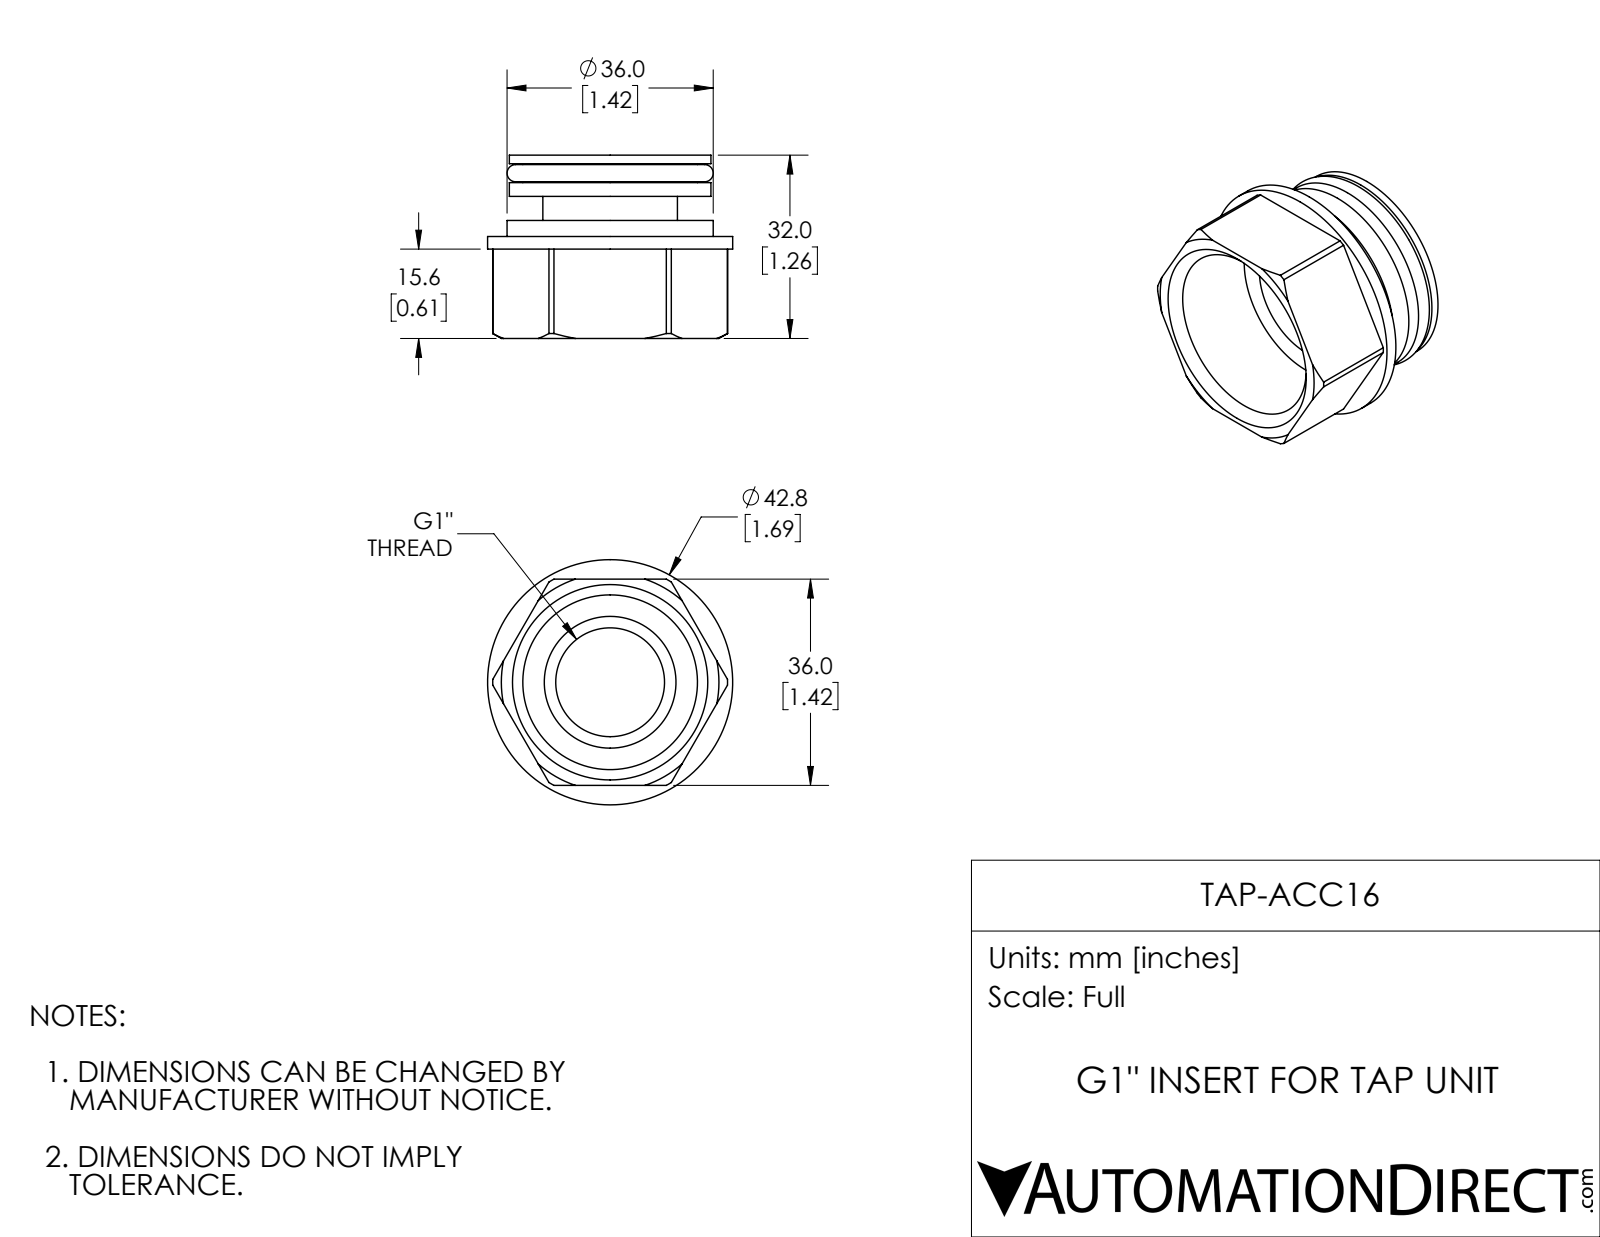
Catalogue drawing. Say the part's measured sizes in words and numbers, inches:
The part is named "TAP-ACC16". Its 3-D file was written by "SolidWorks 2017 (AUTOMOTIVE_DESIGN)". It is 1 solid with 58 faces: 15 planar, 26 cylindrical and 17 other. Overall it measures 1.685 by 1.685 by 1.26 inches. Its volume is 0.877 cubic inches and its surface area 16.13 square inches. Round holes: 1 of diameter 0.748, 1 of diameter 1.024. Round bosses or shafts: 1 of diameter 1.685, 1 of diameter 1.417, 1 of diameter 1.386, 1 of diameter 1.201, 1 of diameter 0.925. Partial cylindrical surfaces (rounded edges, fillets, slot ends): 1 of radius 0.807. The main face-to-face distances are 1.417, 0.165, 0.449, 0.283, 0.11, 0.276, 0.559, 0.087, 0.197, 0.362.
